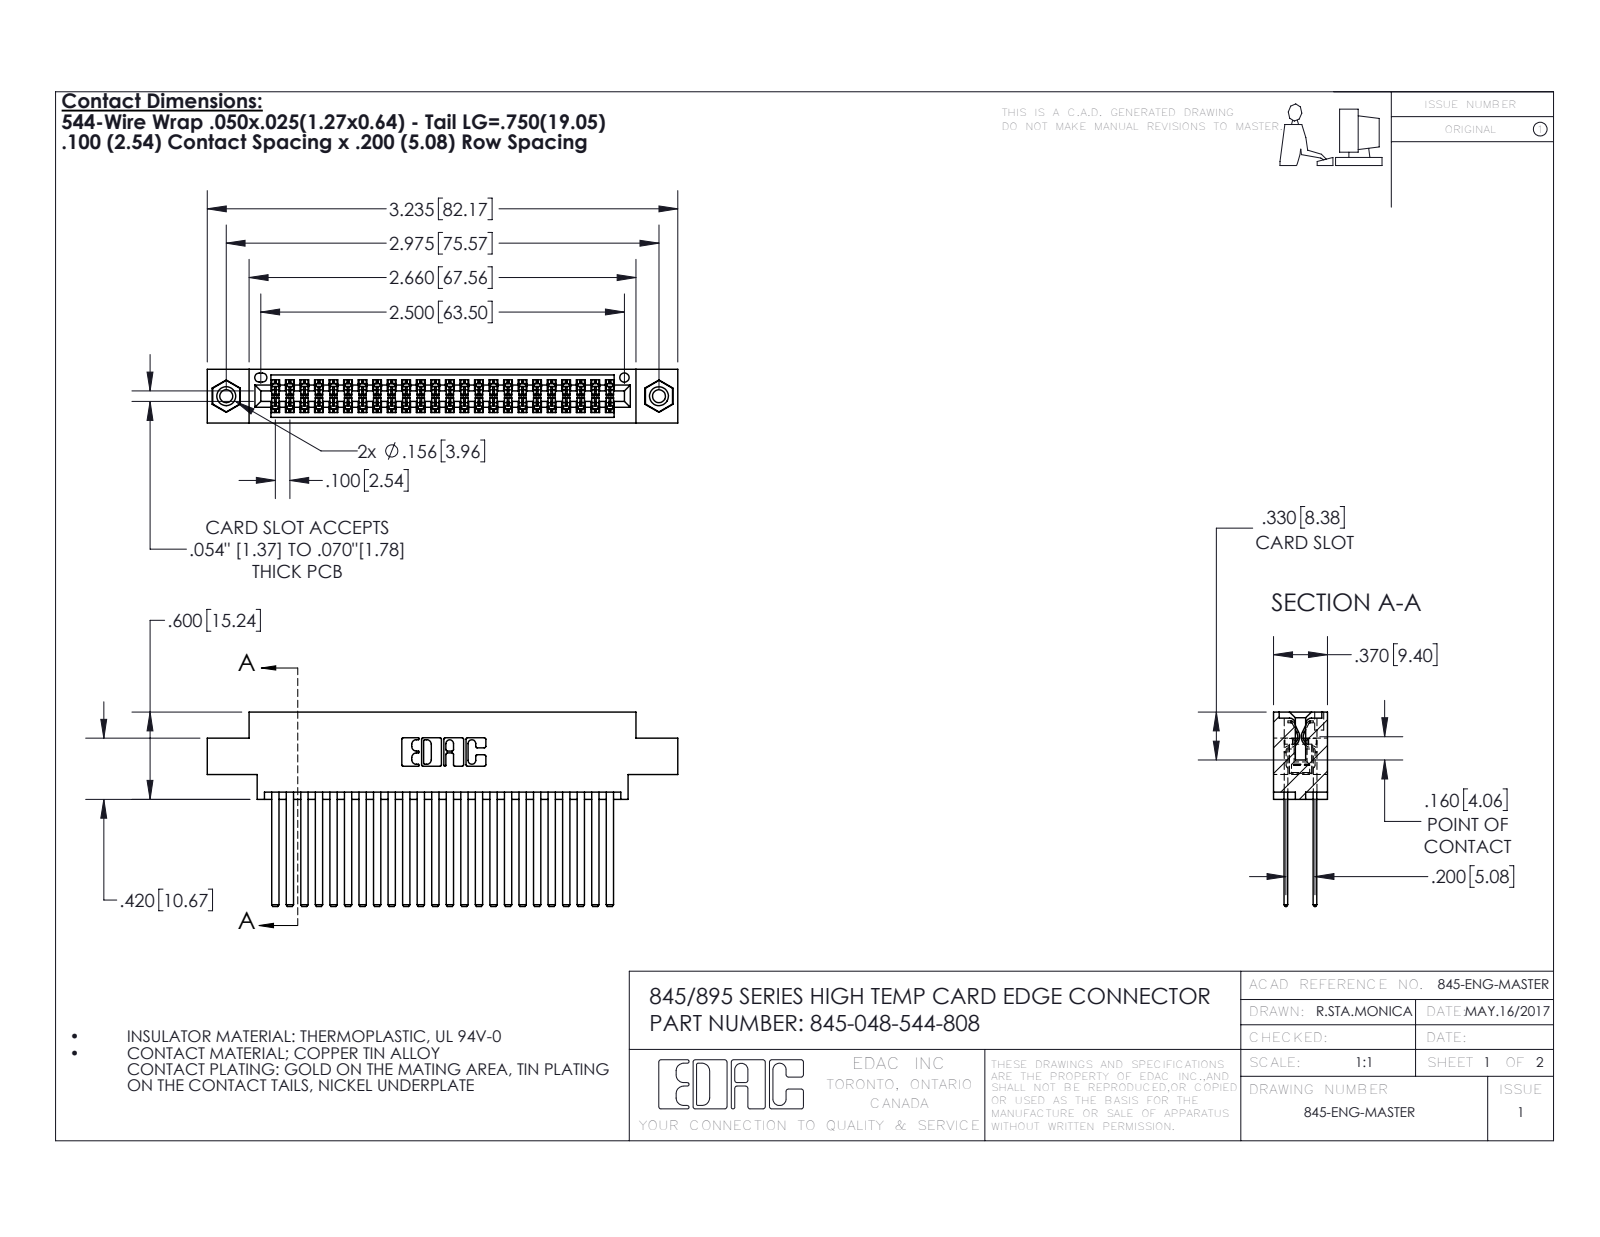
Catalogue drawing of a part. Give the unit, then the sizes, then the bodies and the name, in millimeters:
Units: millimetres
Overall size (bounding box): 82.2 × 34 × 9.4
Round holes (diameter × count): ⌀2.3 ×2, ⌀3.2 ×2, ⌀4 ×2, ⌀1.6 ×1
Round bosses / shafts (diameter × count): ⌀3.9 ×2
Partial cylindrical surfaces — rounded edges, fillets, slot ends (radius × count): R0.2 ×72, R0.3 ×22, R0.2 ×6, R0.8 ×6, R0.7 ×3, R0.4 ×2, R0.5 ×2, R0.6 ×2
Main face-to-face distances: 5.1, 1.8, 7.6, 0.6, 2.5, 6.9, 5.7, 4.4, 9.4, 3.8
Hole centre spacings: 6.9, 69.6, 75.6
Volume: 8 370 mm³ · Surface area: 14 150 mm²
Bodies: 51 solids, 2302 faces (1508 planar, 778 cylindrical, 16 other)
Part name (STEP PRODUCT): 345 Part_0.170 Offset - 0.156 Dia-TI; 345-250-001_345-250-003-102; 345-292-001_345-293-144; 345-048-544-808
STEP written by: SolidWorks 2016 (CONFIG_CONTROL_DESIGN)
